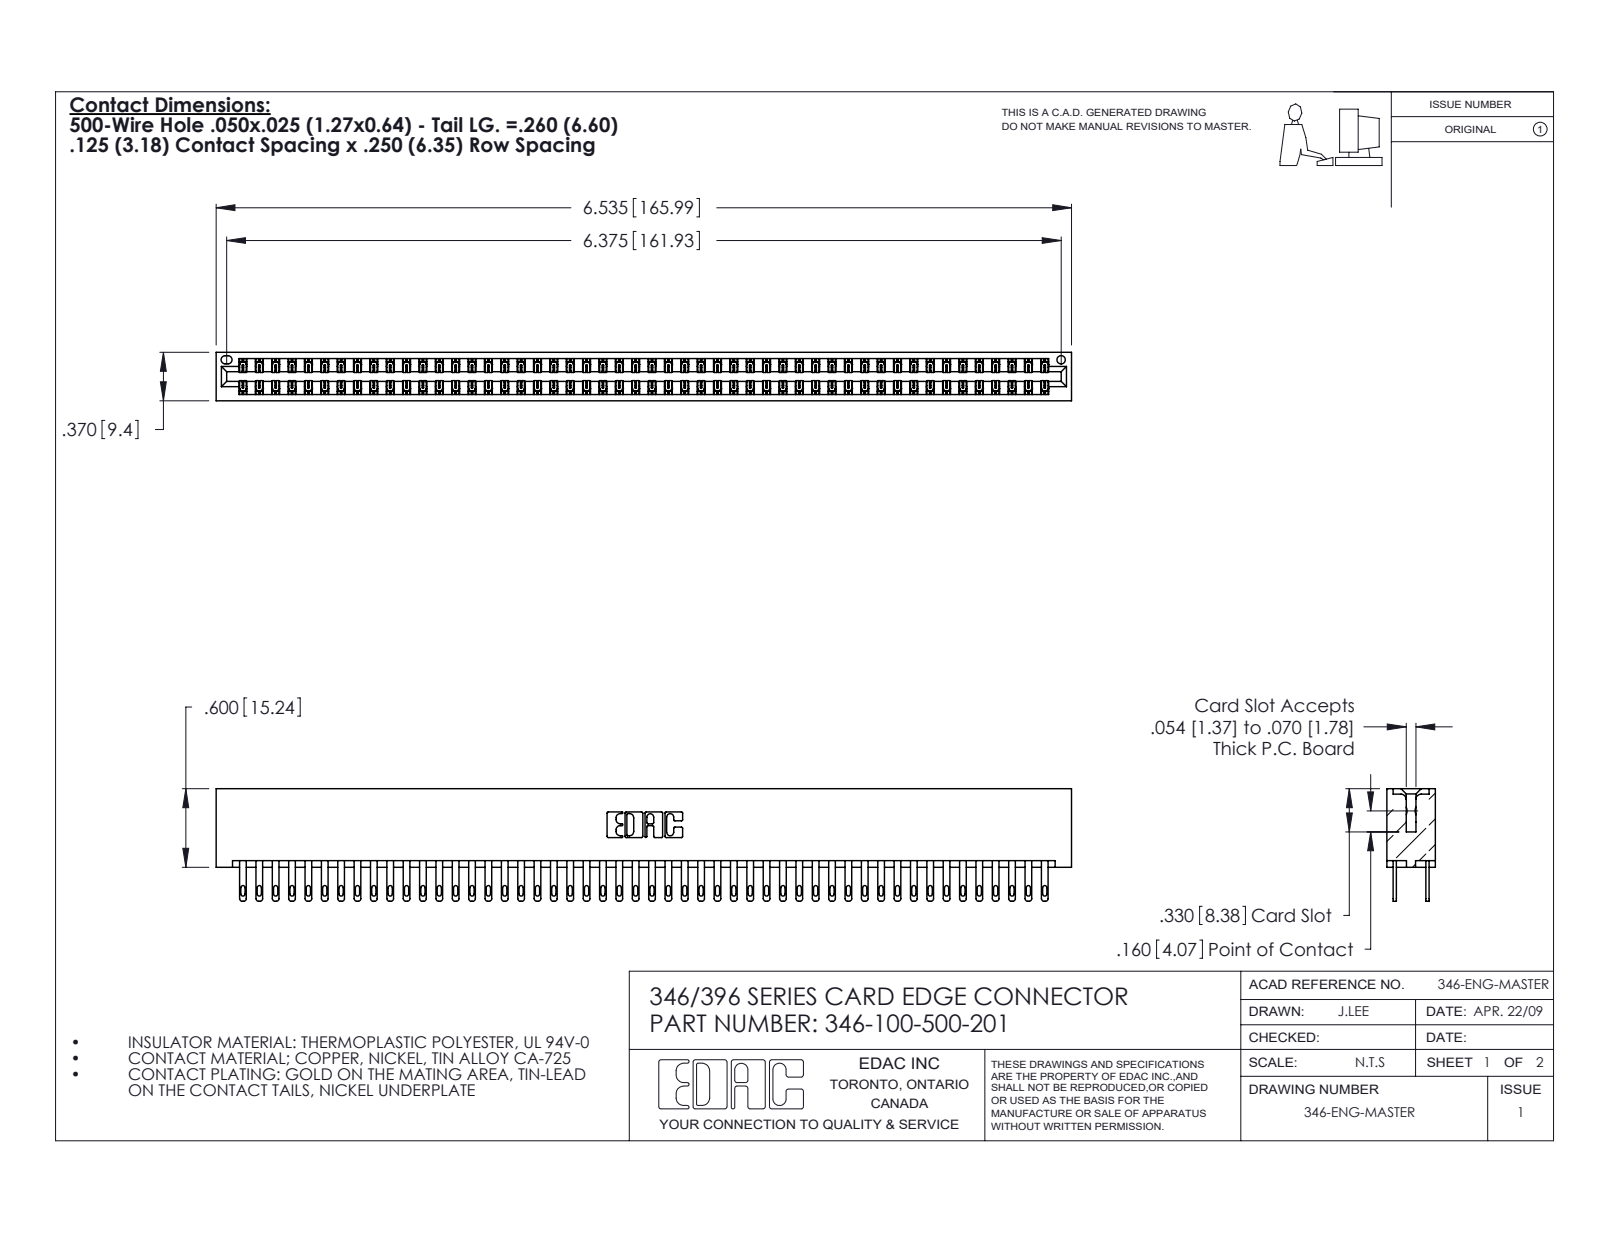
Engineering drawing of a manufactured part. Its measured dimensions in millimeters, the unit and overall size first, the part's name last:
Units: millimetres
Overall size (bounding box): 166 × 21.8 × 9.4
Round holes (diameter × count): ⌀1.6 ×1
Partial cylindrical surfaces — rounded edges, fillets, slot ends (radius × count): R0.2 ×150, R0.4 ×100, R0.5 ×100, R0.3 ×22, R0.2 ×6, R0.8 ×6, R0.7 ×3, R0.4 ×2
Main face-to-face distances: 1.2, 8.2, 6.4, 1.8, 7.6, 0.6, 9.4, 7, 3.8, 5.6
Volume: 17 120 mm³ · Surface area: 24 880 mm²
Bodies: 101 solids, 4914 faces (2972 planar, 1942 cylindrical, 0 other)
Part name (STEP PRODUCT): 345-292-001_345-293-100; 346-100-500-201; 346 Part_No Mounting Lugs
STEP written by: SolidWorks 2020 (CONFIG_CONTROL_DESIGN)
